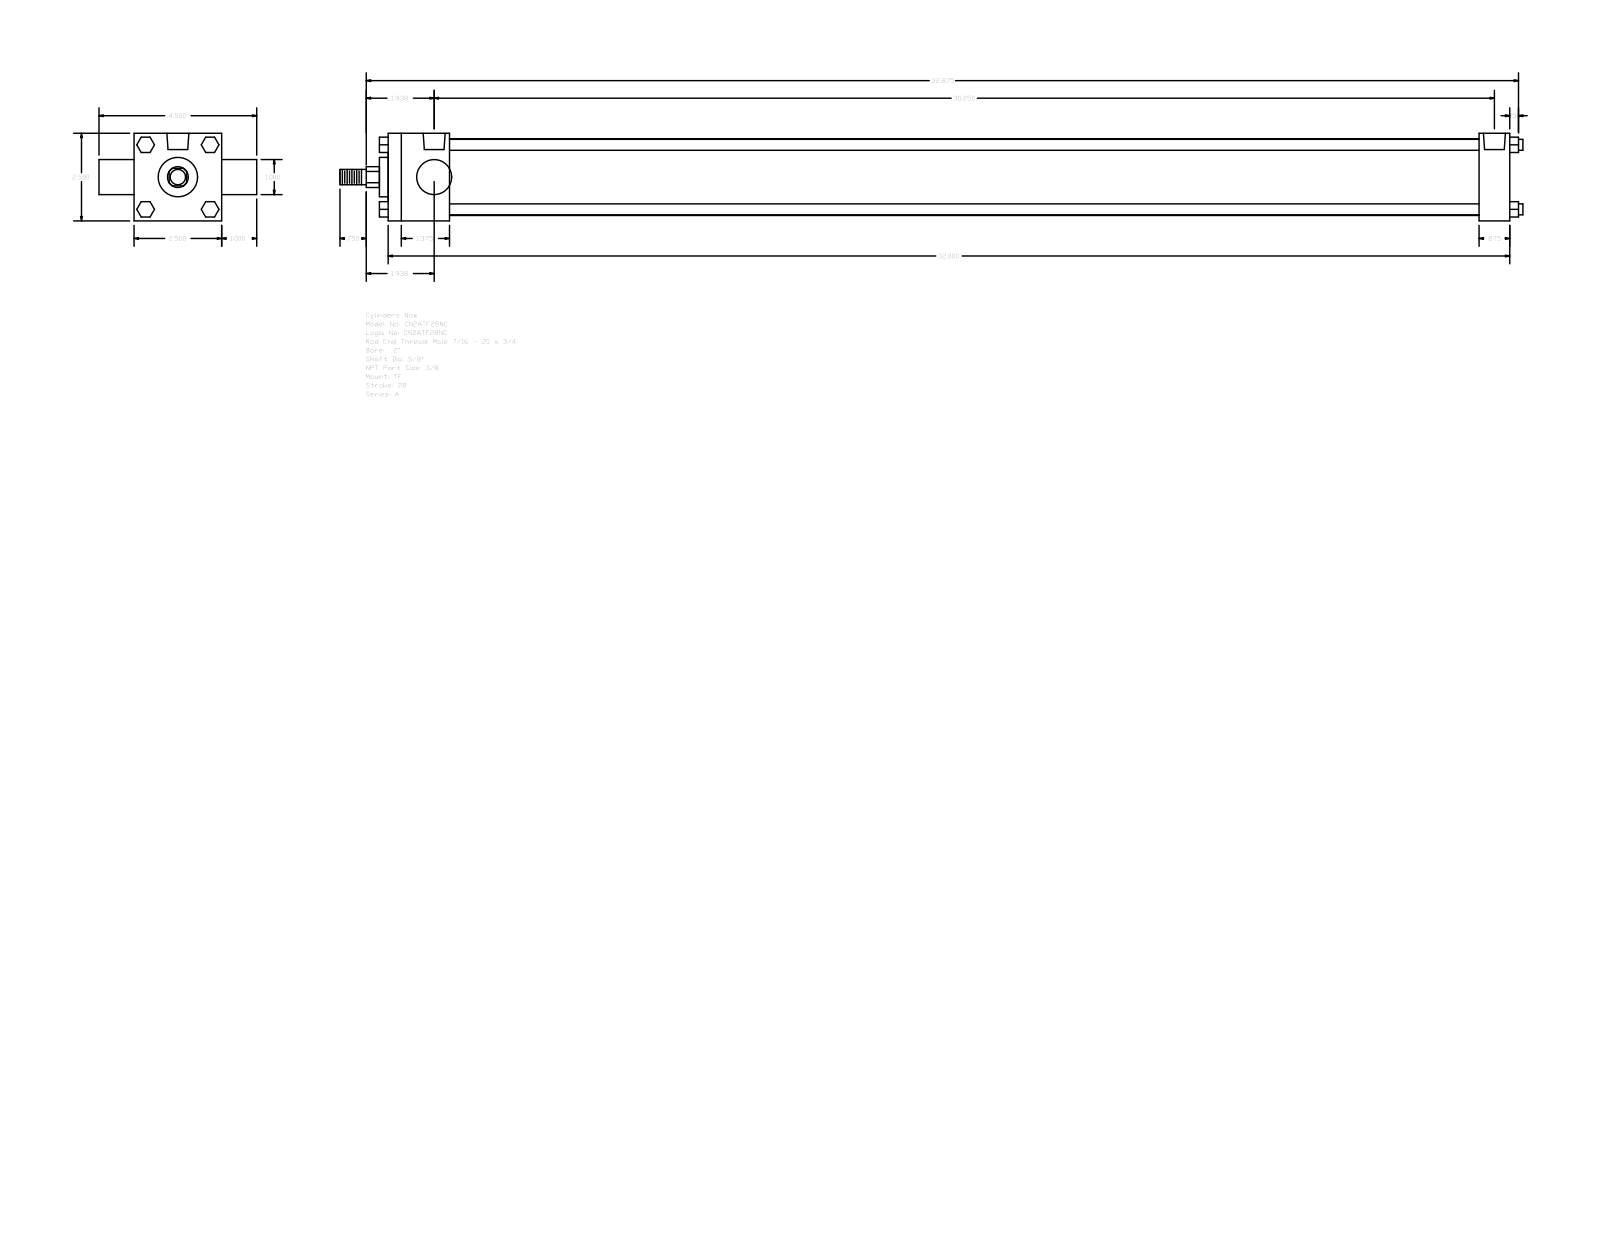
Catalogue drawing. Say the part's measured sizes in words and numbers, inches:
The part is named "A_TF__0200_0.625". Its 3-D file was written by "GSSL Pune (CONFIG_CONTROL_DESIGN)". It is 0 solids with 120 faces: 92 planar, 28 cylindrical and 0 other. Overall it measures 33.75 by 4.5 by 2.5 inches. Round holes: 3 of diameter 0.219, 2 of diameter 0.627. Round bosses or shafts: 4 of diameter 0.313, 1 of diameter 2.19, 1 of diameter 1.125, 1 of diameter 1, 1 of diameter 0.625, 1 of diameter 0.437. Partial cylindrical surfaces (rounded edges, fillets, slot ends): 1 of radius 0.297. The main face-to-face distances are 2.5, 32, 1.75, 31.125, 29.375, 30.25, 0.875, 1, 3.5, 0.25. The hole center spacings are 0.156, 0.157, 29.937, 30.093, 30.094, 30.25.
